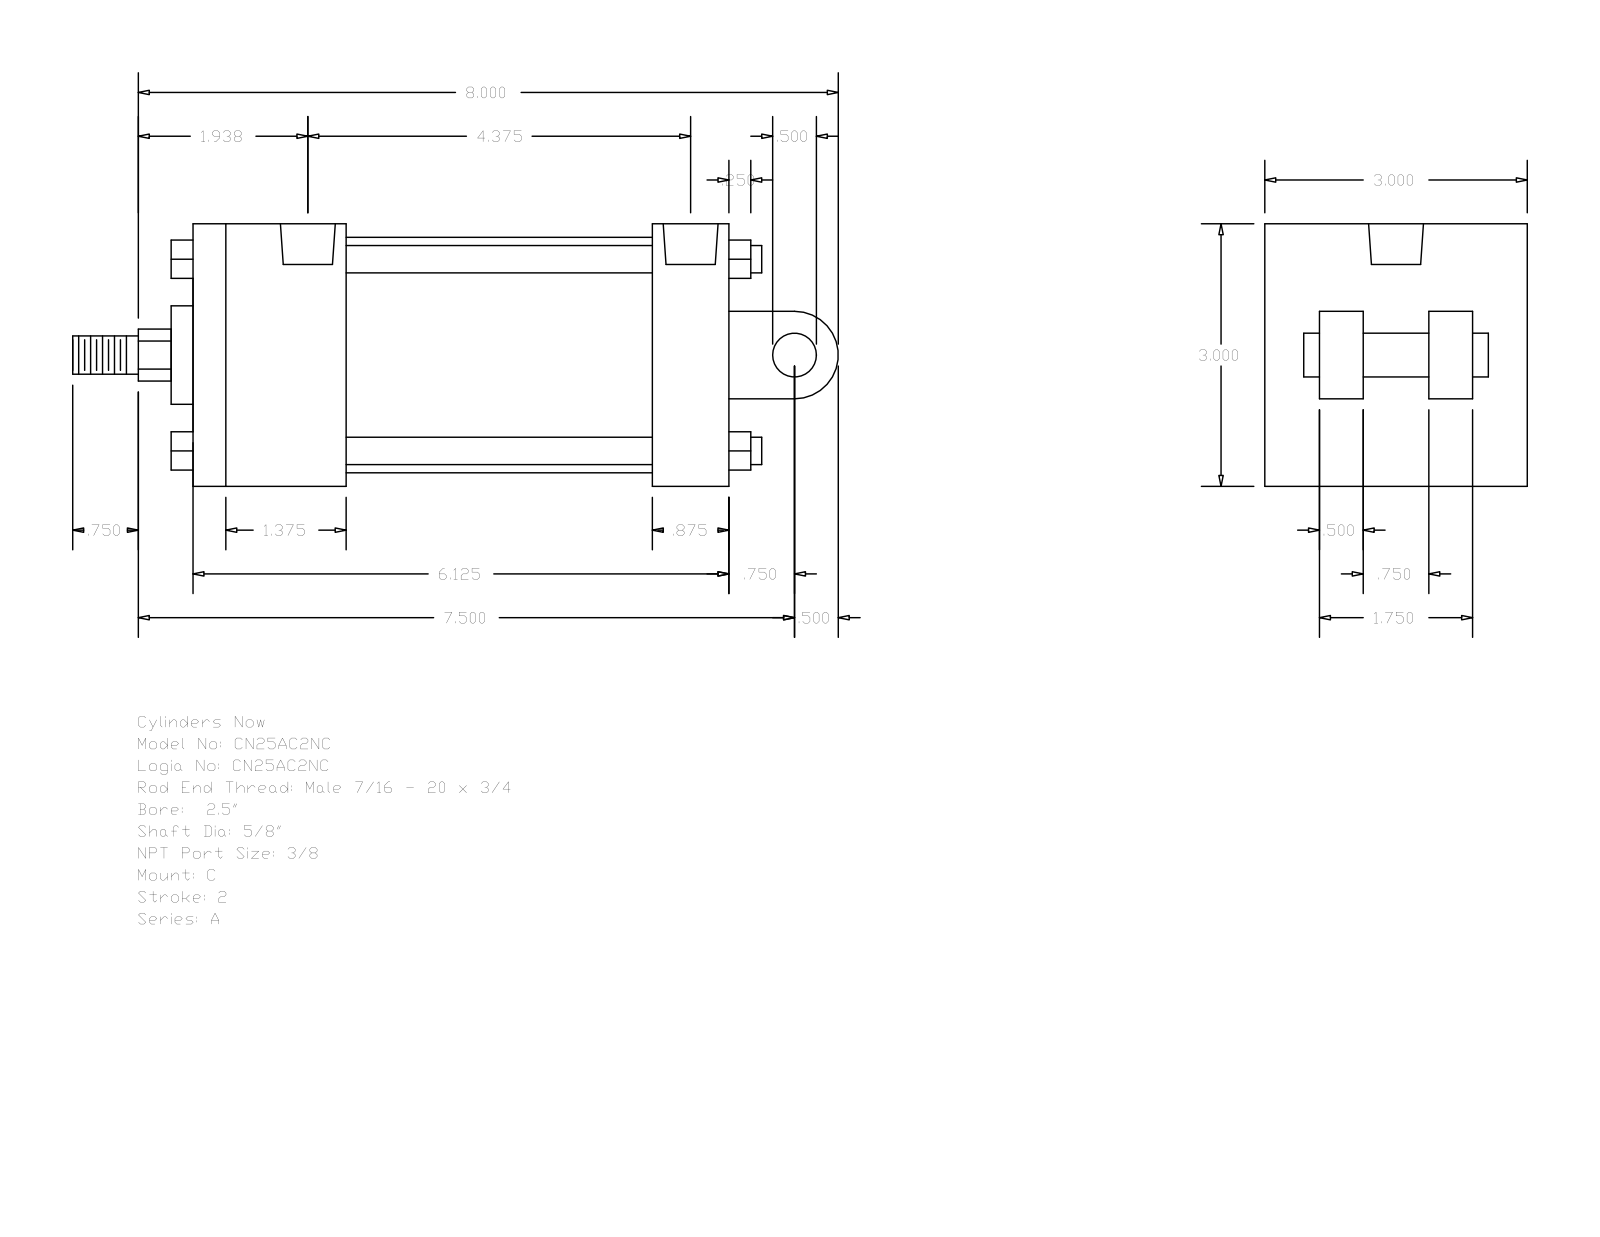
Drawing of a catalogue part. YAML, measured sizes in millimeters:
part_name: "A_C__0250_0.625"
step_written_by: "GSSL Pune (CONFIG_CONTROL_DESIGN)"
units: millimeters
bodies: {solids: 0, faces: 135, planar: 102, cylindrical: 33, other: 0}
overall_size: [222.25, 76.2, 76.2]
round_holes:
  - {diameter: 5.56, count: 4}
  - {diameter: 15.93, count: 2}
round_bosses_or_shafts:
  - {diameter: 7.94, count: 4}
  - {diameter: 68.33, count: 1}
  - {diameter: 28.57, count: 1}
  - {diameter: 15.88, count: 1}
  - {diameter: 12.7, count: 1}
  - {diameter: 11.11, count: 1}
partial_cylinders:
  - {radius: 7.54, count: 1}
  - {radius: 12.7, count: 1}
face_to_face_distances: [76.2, 155.57, 44.45, 133.34, 88.89, 111.12, 22.23, 50.8, 12.7, 25.4]
hole_center_spacings: [2.38, 113.51, 115.89, 111.13]
